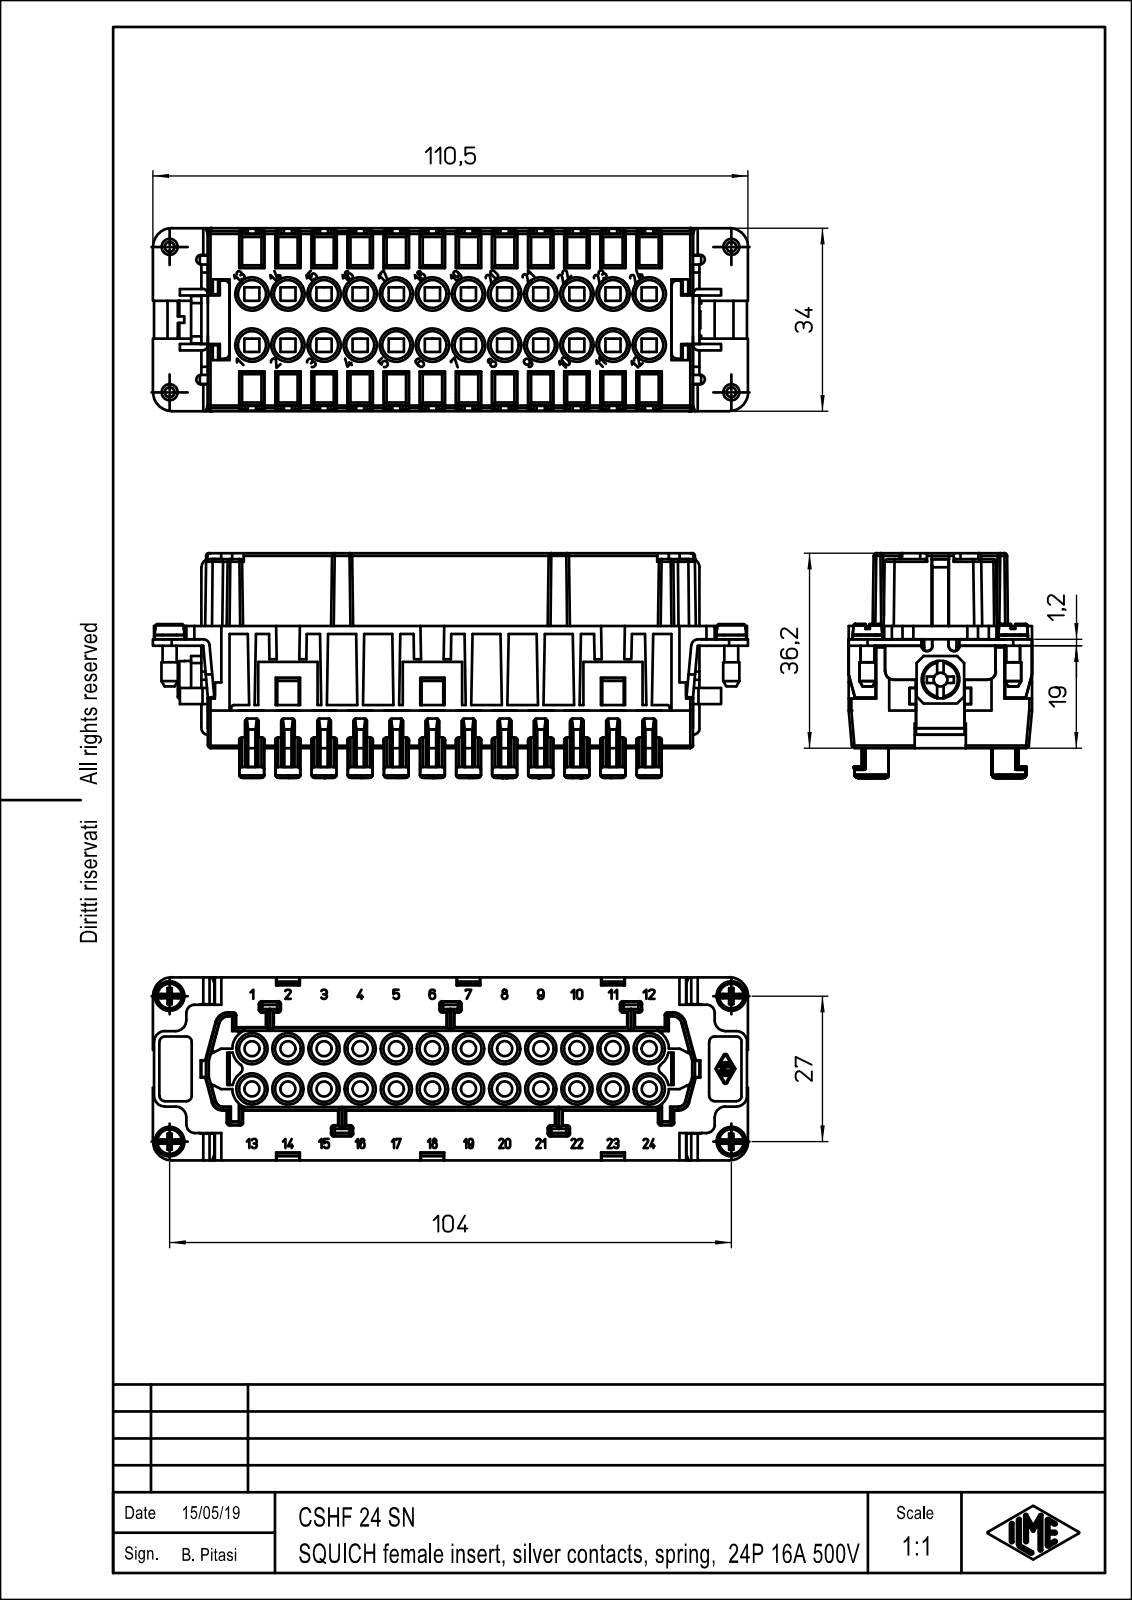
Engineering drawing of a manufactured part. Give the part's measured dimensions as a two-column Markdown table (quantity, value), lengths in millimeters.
| quantity | value |
| --- | --- |
| part name | CSHF_24_SN |
| STEP written by | Creo Elements/Direct Modeling 20.1B 02-Apr-2019 (C) Parametric Technology GmbH (AUTOMOTIVE_DESIGN) |
| units | millimeters |
| bodies | 1 solid, 2493 faces (1751 planar, 550 cylindrical, 192 other) |
| overall size | 110.4 × 41.7 × 34 |
| volume | 79 455 mm³ |
| surface area | 39 170 mm² |
| round holes (diameter × count) | 2.8 × 28, 5.2 × 24, 5.8 × 24, 2.58 × 1, 4.2 × 1 |
| round bosses / shafts (diameter × count) | 5.5 × 4, 3 × 4, 2.6 × 4, 7 × 1, 6 × 1, 4 × 1 |
| partial cylindrical surfaces (radius × count) | 0.5 × 118, 0.3 × 56, 1.15 × 24, 1 × 20, 1.5 × 10, 2 × 10, 1.2 × 6, 0.88 × 4 |
| main face-to-face distances | 1.5, 13.4, 6.7, 1.2, 32.5, 22.7, 12.5, 20.1, 26.8, 33.5 |
| hole center spacings | 6.7, 10.06, 13.4, 15.36, 20.1, 21.45, 26.8, 27.83 |
